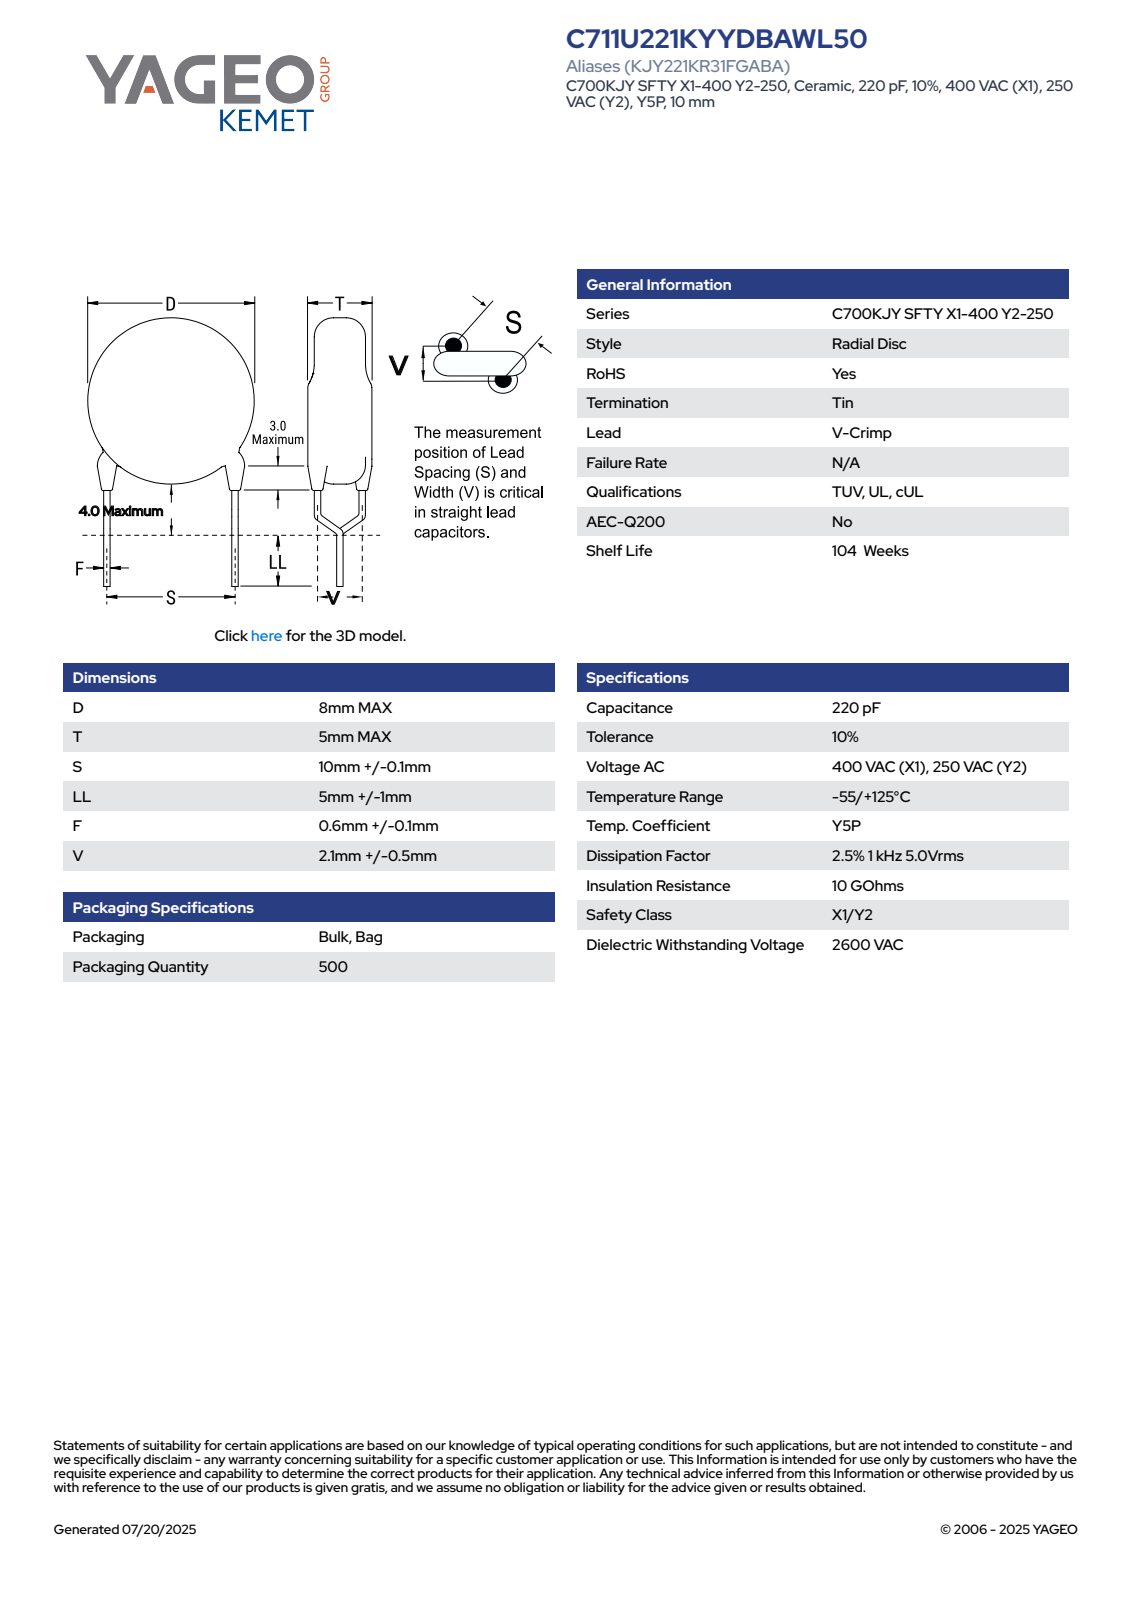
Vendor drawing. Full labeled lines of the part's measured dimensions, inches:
Part name (STEP PRODUCT): CCD_VC8X5_D8T5S10LL6F0.7V2.1
STEP written by: SolidWorks 2021 (AUTOMOTIVE_DESIGN)
Units: inches
Bodies: 4 solids, 89 faces (63 planar, 22 cylindrical, 4 other)
Overall size (bounding box): 0.551 × 0.441 × 0.197
Volume: 0.015 in³ · Surface area: 0.401 in²
Round bosses / shafts (diameter × count): ⌀0.028 ×6, ⌀0.047 ×4, ⌀0.315 ×1
Main face-to-face distances: 0.197, 0.236, 0.038, 0.419, 0.182, 0.38, 0.144, 0.014, 0.031, 0.014
